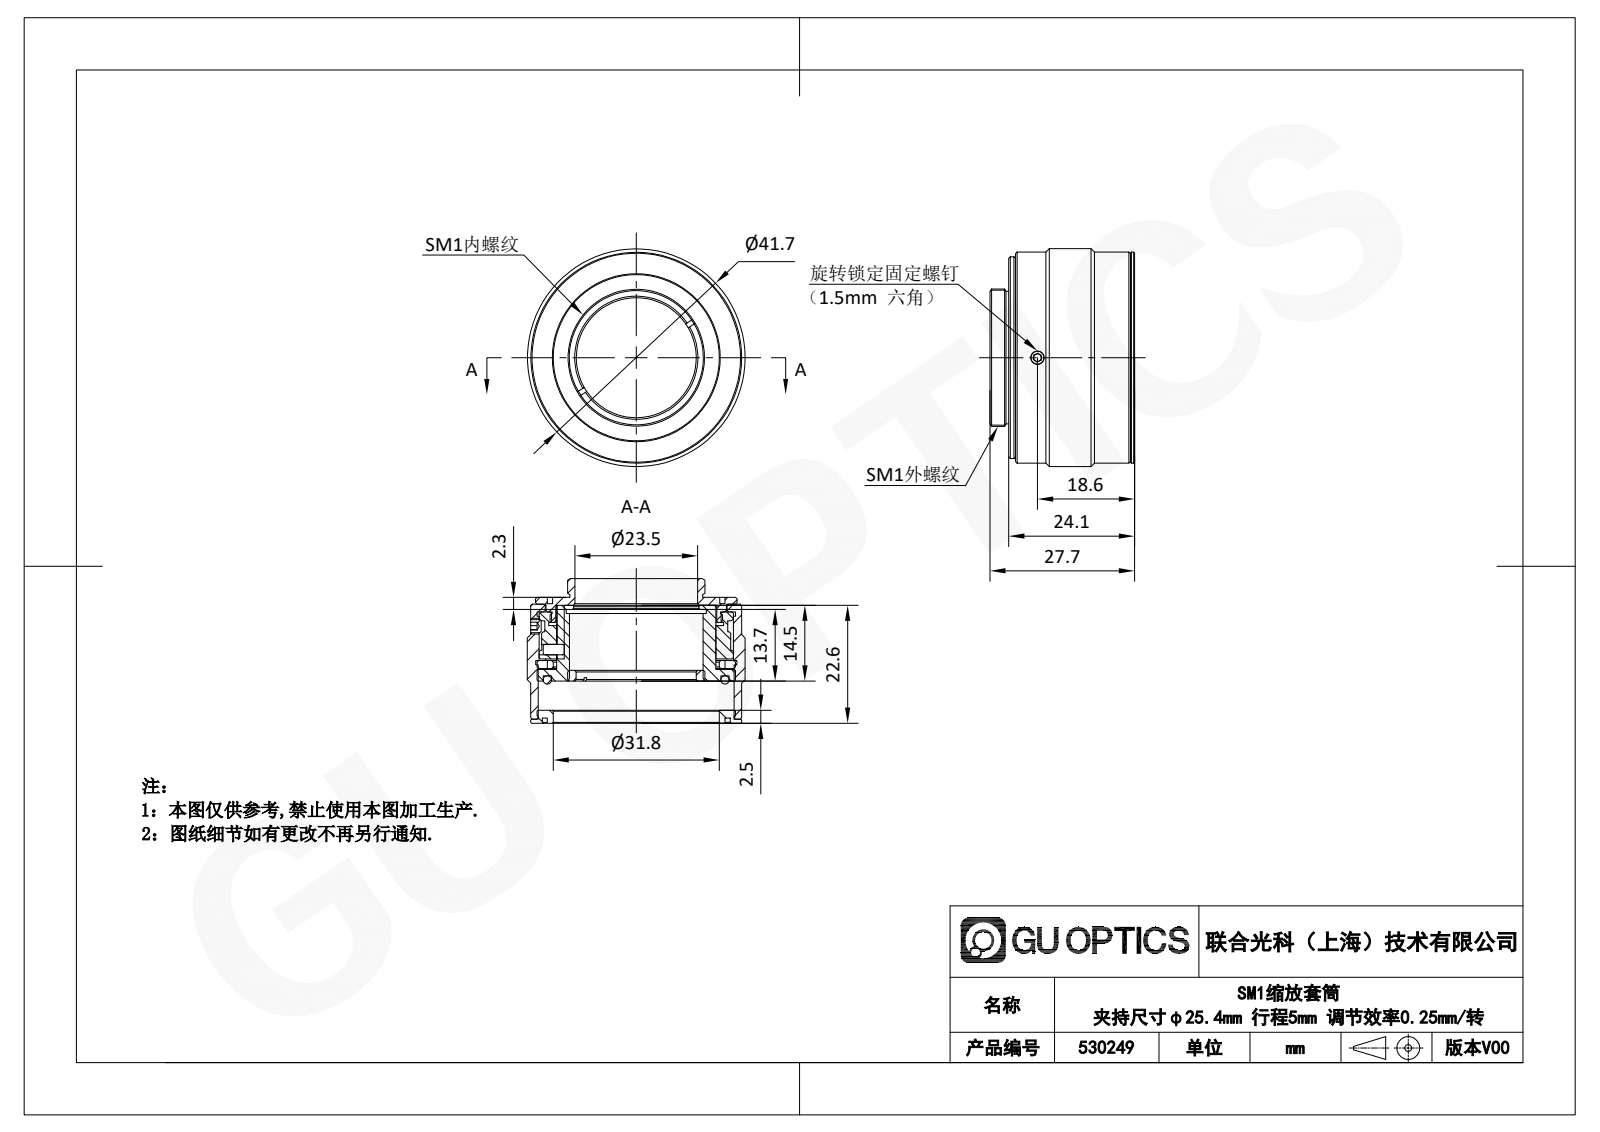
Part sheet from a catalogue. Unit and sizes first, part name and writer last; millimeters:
Units: millimetres
Overall size (bounding box): 41.7 × 41.7 × 27.7
Round holes (diameter × count): ⌀1 ×6, ⌀1.6 ×2, ⌀2 ×1, ⌀2.5 ×1, ⌀23 ×1, ⌀23.5 ×1, ⌀24 ×1, ⌀25.6 ×1, ⌀26.8 ×1, ⌀30.5 ×1, ⌀30.8 ×1, ⌀31.8 ×1
Round bosses / shafts (diameter × count): ⌀41.7 ×1, ⌀40.4 ×1, ⌀38.6 ×1, ⌀38 ×1, ⌀37.2 ×1, ⌀36.2 ×1, ⌀35 ×1, ⌀34.6 ×1
Partial cylindrical surfaces — rounded edges, fillets, slot ends (radius × count): R1 ×1
Main face-to-face distances: 1.5, 12.3, 1.3, 1.7, 10.3, 9.5, 10.5, 16, 10.8, 12.1
Hole centre spacings: 0.5, 16.5, 23.33, 23.69, 24.05, 34, 1, 17
Volume: 14 835 mm³ · Surface area: 19 198 mm²
Bodies: 11 solids, 185 faces (76 planar, 54 cylindrical, 55 other)
Part name (STEP PRODUCT): GB／T119-2000圆柱销A型2×4; GB／T77-2000内六角平端紧定螺钉M3×2; SM1ZT-6; SM1R (+6 more)
STEP written by: SolidWorks 2020 (CONFIG_CONTROL_DESIGN)
